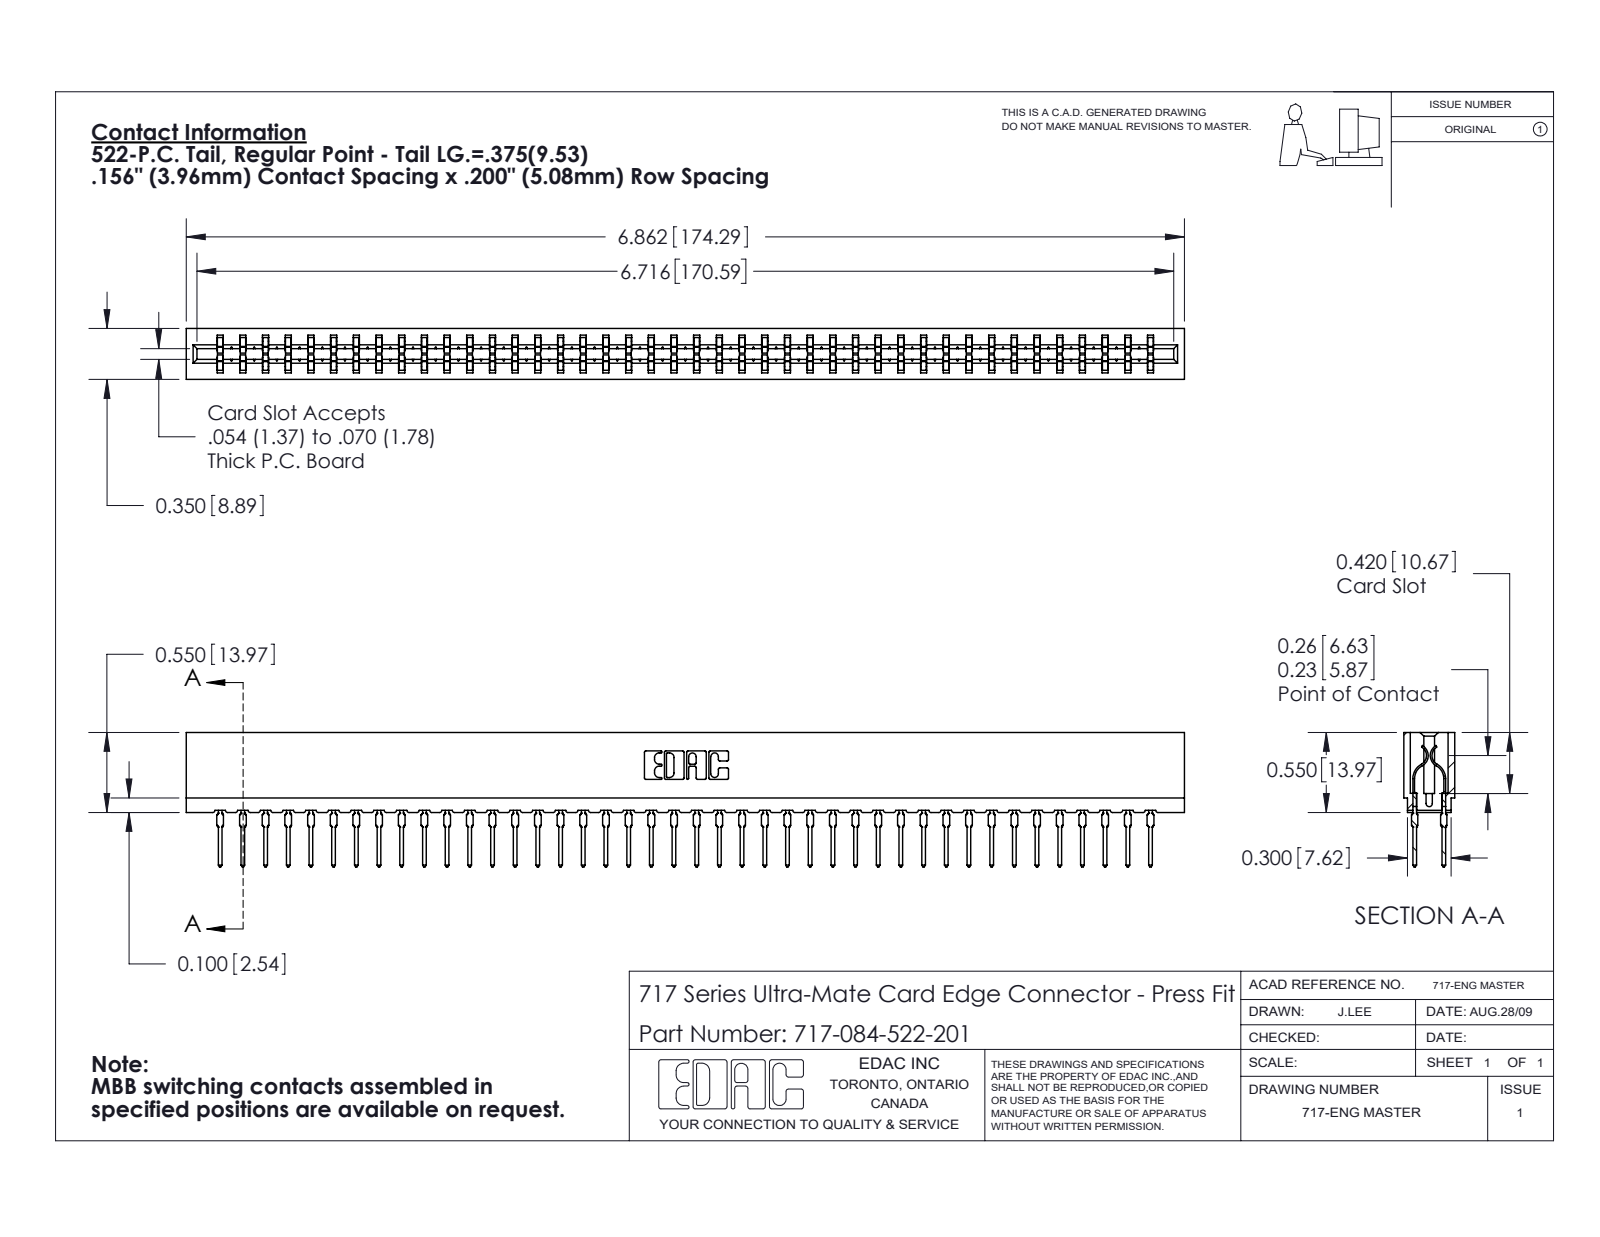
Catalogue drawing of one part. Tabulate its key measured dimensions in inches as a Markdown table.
| quantity | value |
| --- | --- |
| part name | 745-292-001_522; 717 Part_Insulator Option - 06; 717-084-522-201 |
| STEP written by | SolidWorks 2020 (CONFIG_CONTROL_DESIGN) |
| units | inches |
| bodies | 85 solids, 7654 faces (3960 planar, 1510 cylindrical, 2184 other) |
| overall size | 6.862 × 0.924 × 0.35 |
| volume | 0.927 in³ |
| surface area | 36.54 in² |
| partial cylindrical surfaces (radius × count) | 0.021 × 168, 0.015 × 84, 0.01 × 22, 0.005 × 8, 0.011 × 8, 0.007 × 6, 0.031 × 6, 0.026 × 3 |
| main face-to-face distances | 0.212, 0.138, 0.35, 0.063, 0.287, 0.076, 0.149, 0.074, 0.045, 0.305 |
